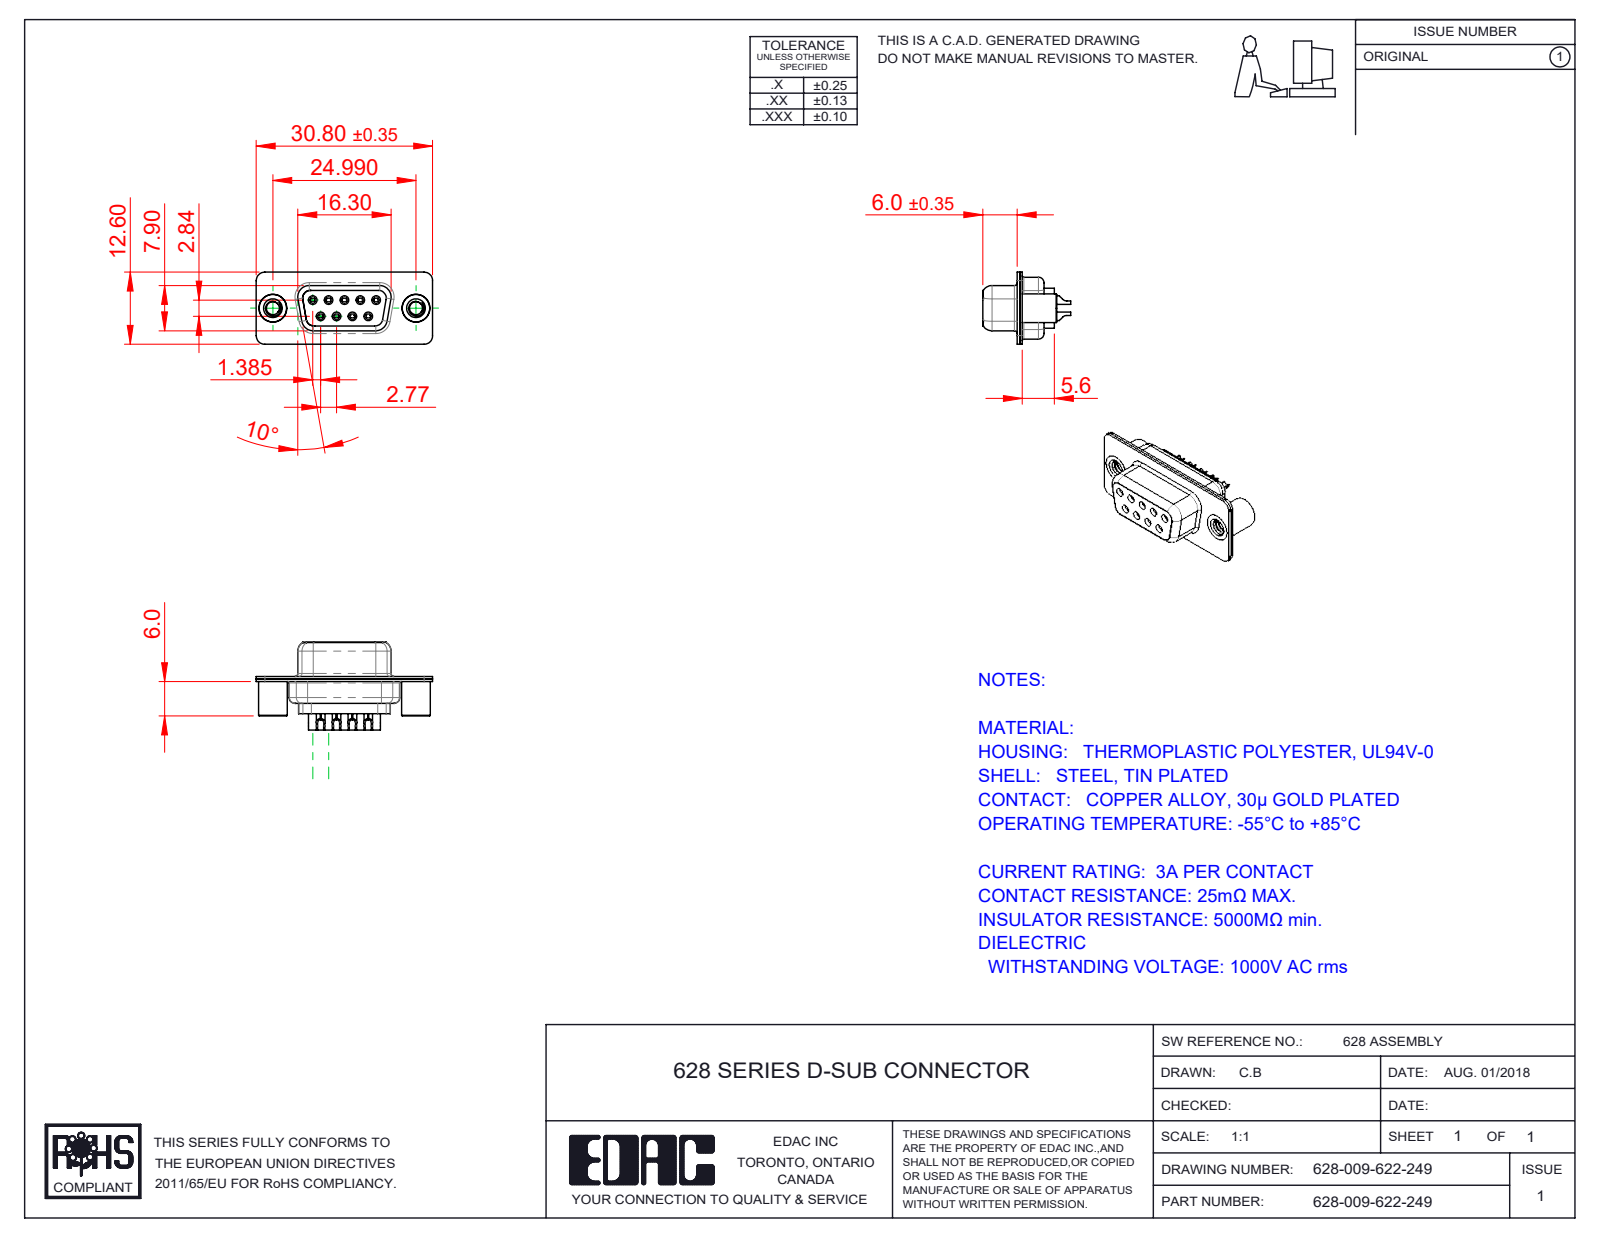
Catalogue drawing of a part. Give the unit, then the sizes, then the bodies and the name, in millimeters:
Units: millimetres
Overall size (bounding box): 30.8 × 15.35 × 12.6
Round holes (diameter × count): ⌀0.8 ×9, ⌀0.9 ×9, ⌀1.1 ×9, ⌀1.6 ×9, ⌀1.7 ×5, ⌀2.26 ×2, ⌀4 ×2, ⌀4.05 ×2, ⌀4.85 ×2
Round bosses / shafts (diameter × count): ⌀2 ×9, ⌀1.5 ×9, ⌀1.2 ×9, ⌀5 ×2, ⌀4.95 ×2, ⌀4.8 ×2
Partial cylindrical surfaces — rounded edges, fillets, slot ends (radius × count): R1.5 ×17, R2 ×12, R0.28 ×9, R1 ×6, R1.35 ×6, R0.25 ×4, R0.5 ×4, R0.6 ×4
Main face-to-face distances: 0.45, 0.4, 0.9, 1.9, 8.5, 6.6, 1.4, 6.5, 0.5, 7.05
Hole centre spacings: 3.16, 2.77, 5.54, 5.03, 5.04, 8.31, 7.48, 7.49
Volume: 1 858 mm³ · Surface area: 4 715 mm²
Bodies: 14 solids, 1102 faces (256 planar, 382 cylindrical, 464 other)
Part name (STEP PRODUCT): 628 Contact Row 1_22L; 628 Contact Row 2_22L; 628 4-40 Threaded Standoff BS; 628 Shell Front_09 Contacts (+3 more)
STEP written by: SolidWorks 2020 (CONFIG_CONTROL_DESIGN)
